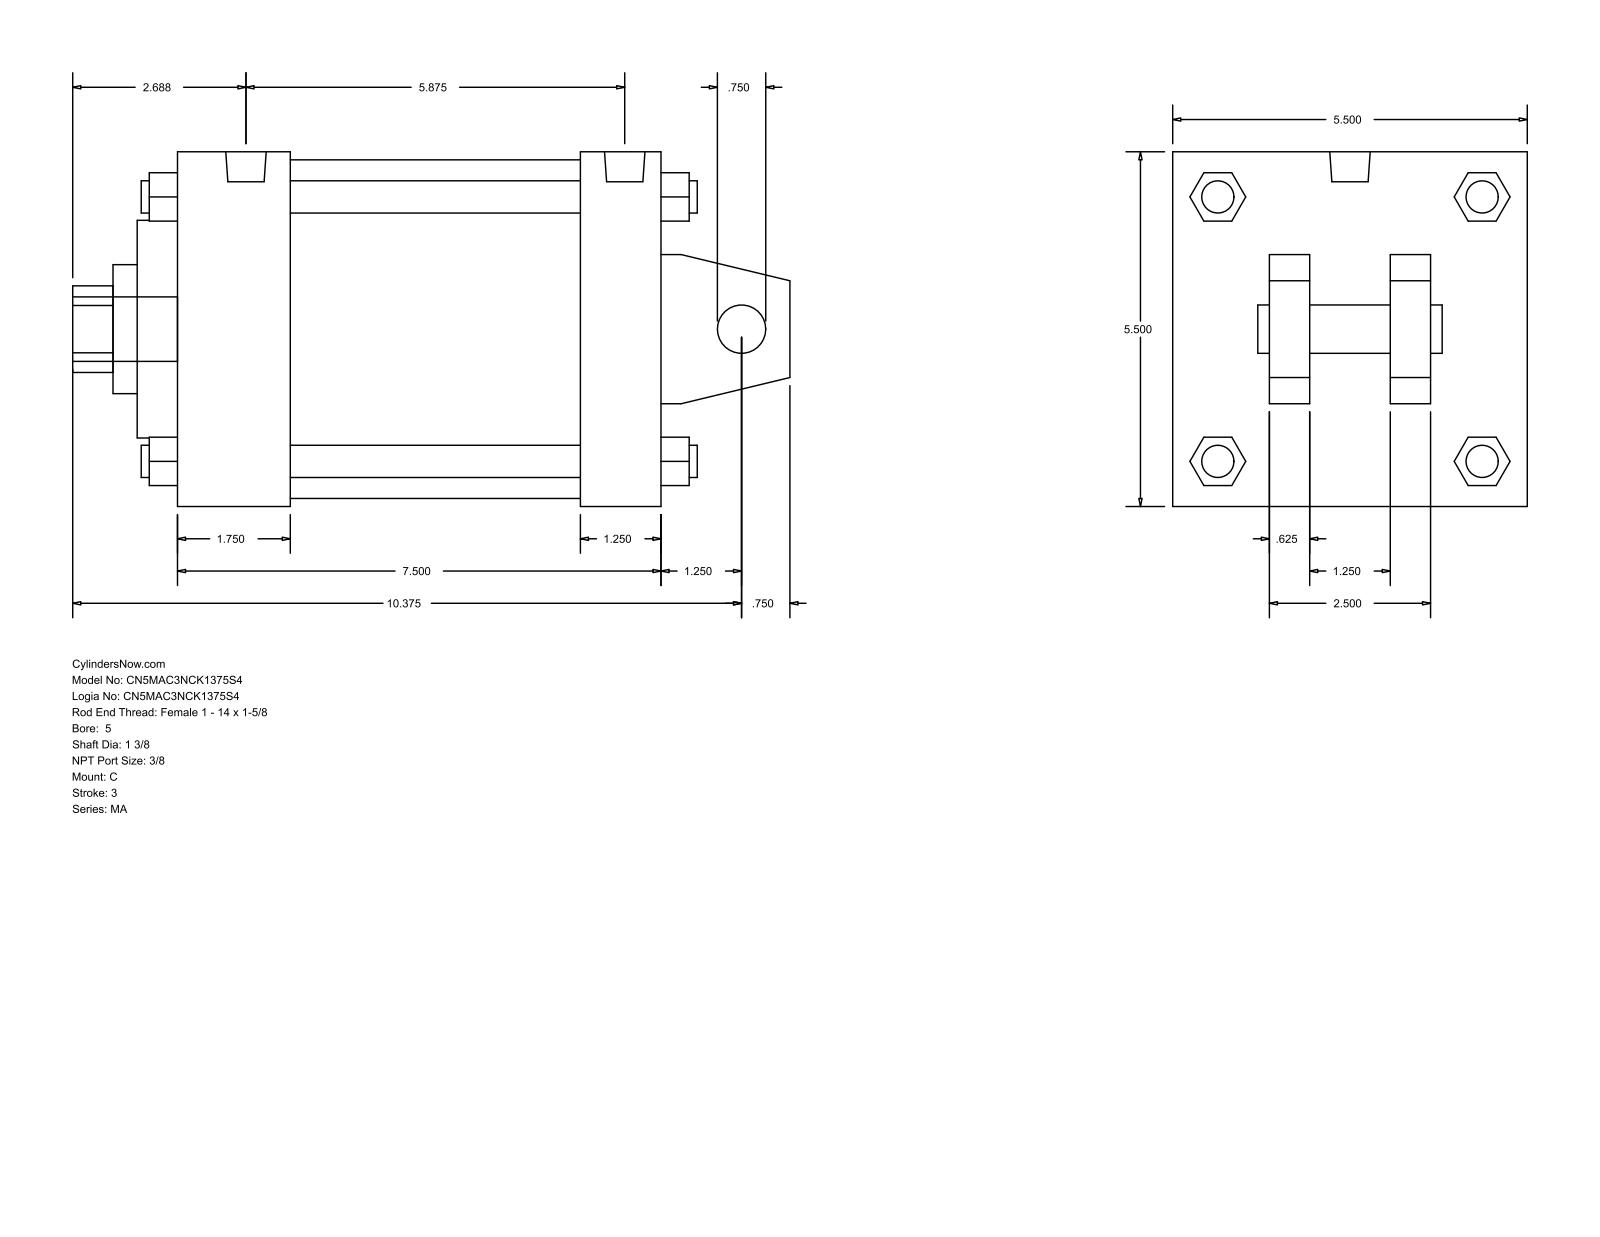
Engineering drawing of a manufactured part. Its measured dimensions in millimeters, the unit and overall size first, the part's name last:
Units: millimetres
Overall size (bounding box): 282.57 × 139.7 × 139.7
Round holes (diameter × count): ⌀19.05 ×1, ⌀34.92 ×1, ⌀50.8 ×1, ⌀85.72 ×1, ⌀133.35 ×1
Round bosses / shafts (diameter × count): ⌀12.7 ×4, ⌀11.11 ×4, ⌀15.93 ×2, ⌀25.4 ×1
Partial cylindrical surfaces — rounded edges, fillets, slot ends (radius × count): R17.06 ×1
Main face-to-face distances: 139.7, 190.51, 15.87, 158.76, 31.75, 44.45, 114.31, 146.06, 38.1, 101.6
Bodies: 0 solids, 141 faces (109 planar, 32 cylindrical, 0 other)
Part name (STEP PRODUCT): MA_C__0500_1.375
STEP written by: GSSL Pune (CONFIG_CONTROL_DESIGN)
